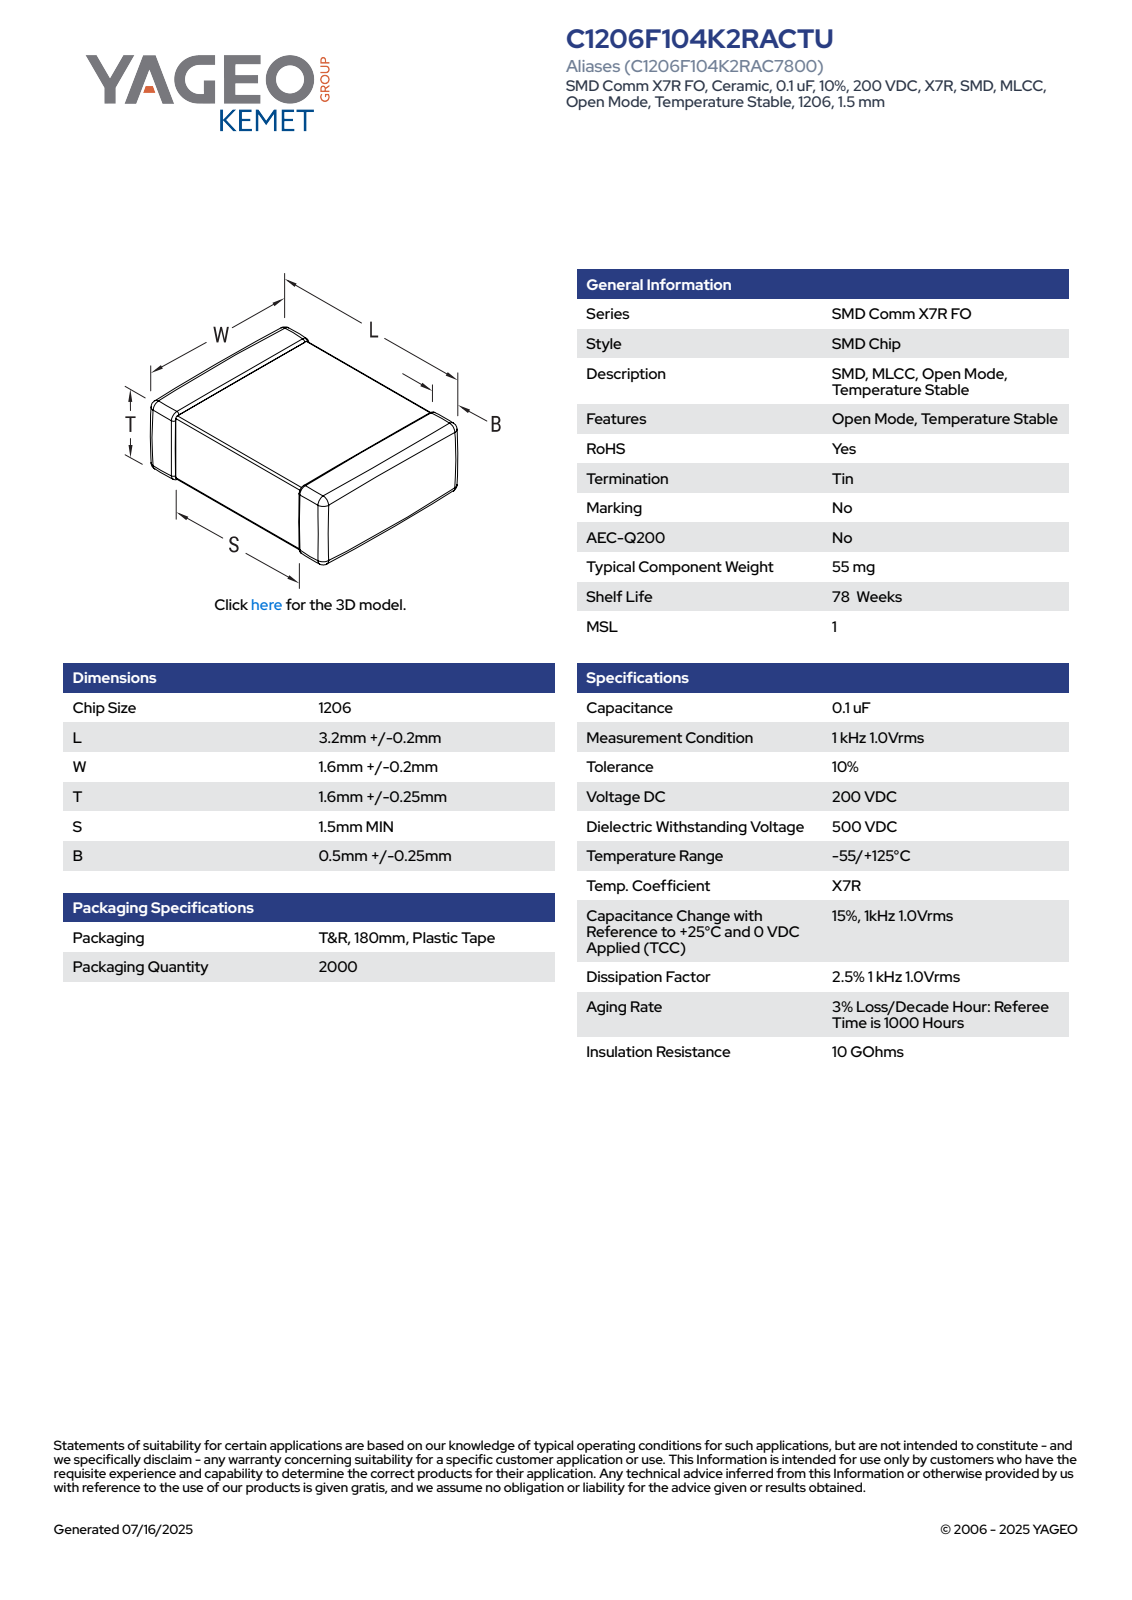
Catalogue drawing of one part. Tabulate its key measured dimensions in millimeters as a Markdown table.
| quantity | value |
| --- | --- |
| part name | CCS_CCSTDNOS_1206_L3.4W1.8T1.85B0.75 |
| STEP written by | SolidWorks 2014 (AUTOMOTIVE_DESIGN) |
| units | millimeters |
| bodies | 4 solids, 125 faces (71 planar, 38 cylindrical, 16 other) |
| overall size | 3.4 × 1.85 × 1.8 |
| volume | 11 mm³ |
| surface area | 31 mm² |
| main face-to-face distances | 1.76, 1.81, 1.72, 1.77, 3.4, 1.8, 1.85, 1.82, 1.78, 0.99 |
